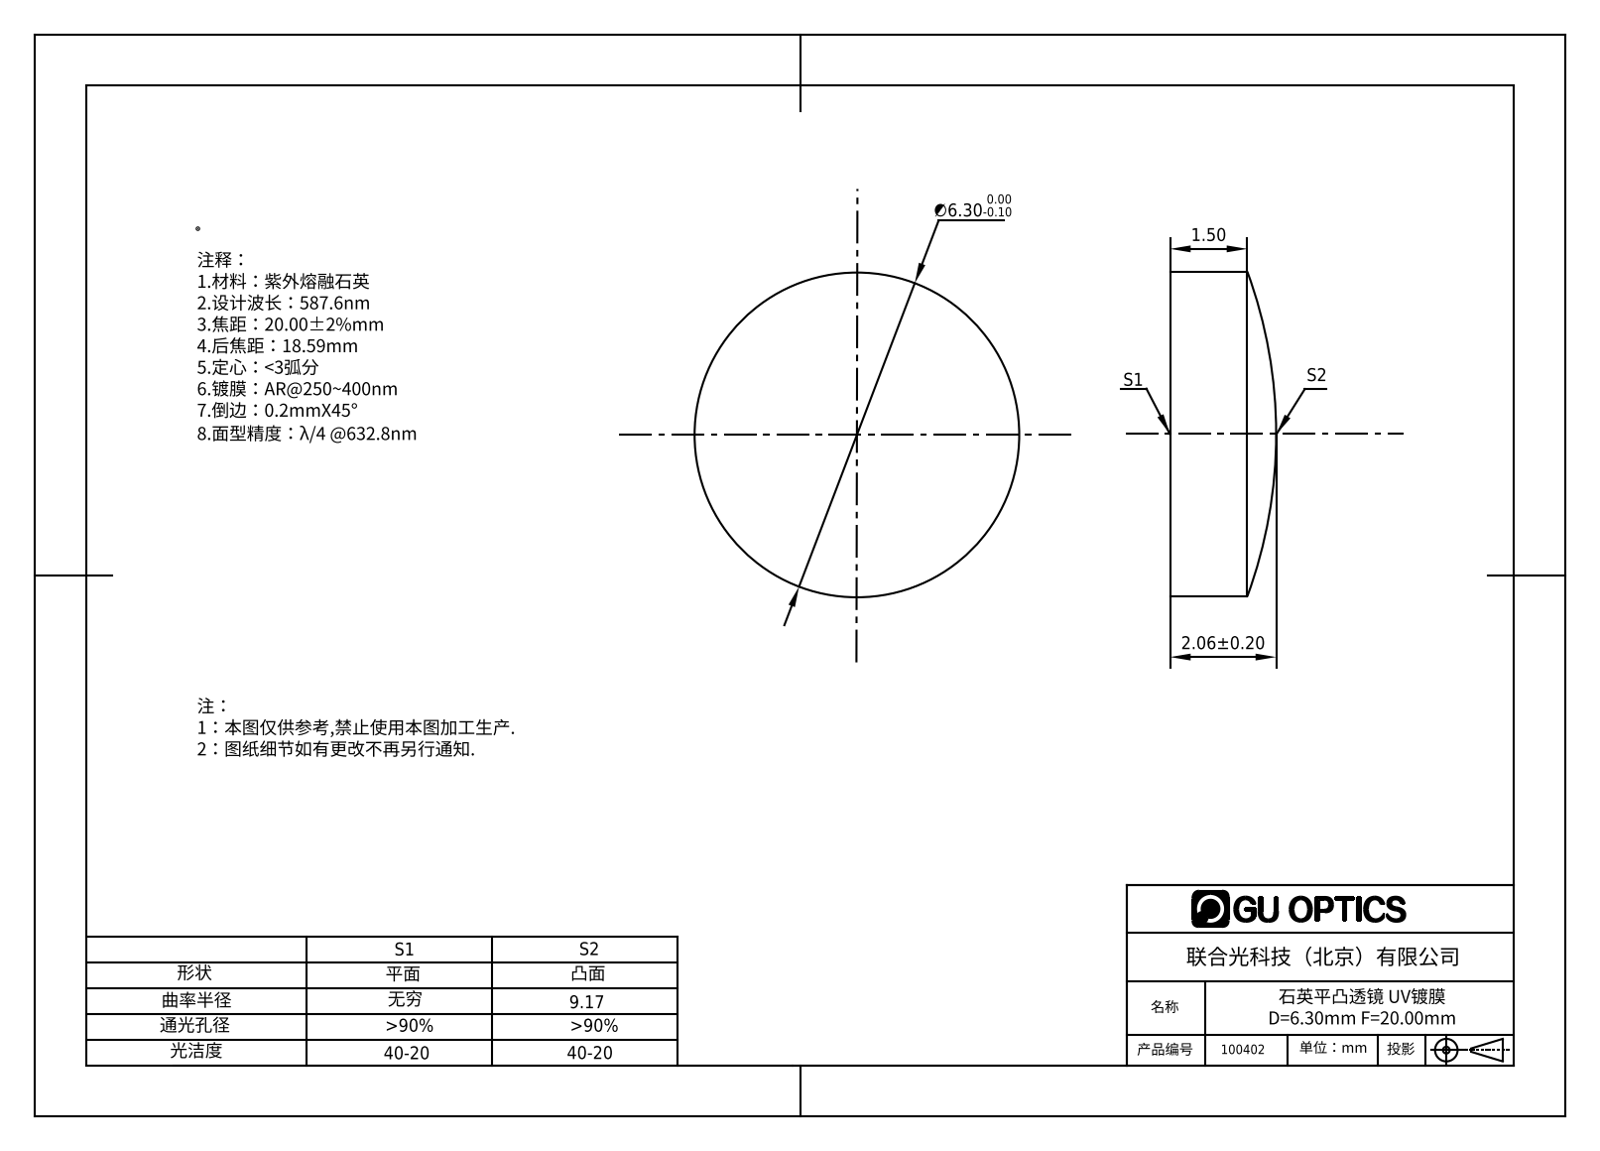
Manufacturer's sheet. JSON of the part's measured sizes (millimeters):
{"part_name": "100352", "step_written_by": "SolidWorks 2016 (AUTOMOTIVE_DESIGN)", "units": "millimeters", "bodies": {"solids": 1, "faces": 5, "planar": 1, "cylindrical": 2, "other": 2}, "overall_size": [6.3, 6.3, 2.06], "volume_mm3": 56, "surface_area_mm2": 93, "round_bosses_or_shafts": [[6.3, 1]]}
